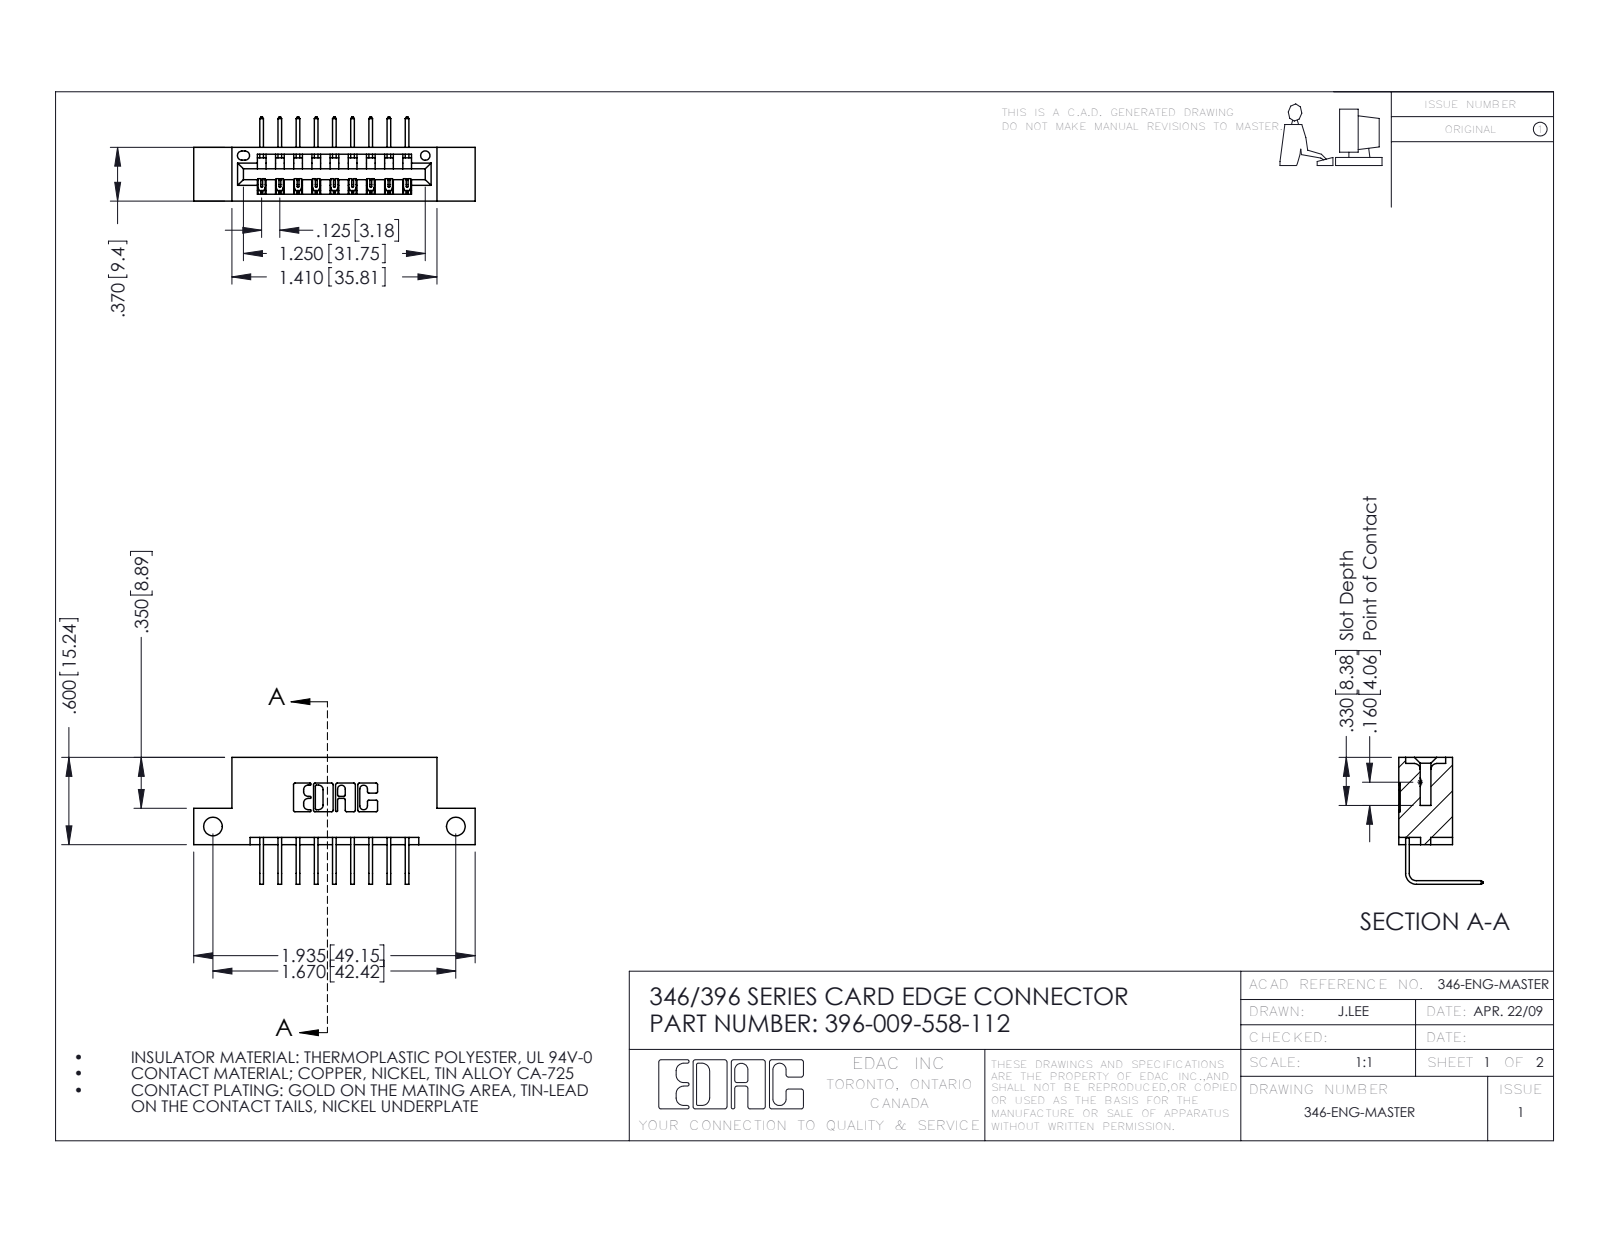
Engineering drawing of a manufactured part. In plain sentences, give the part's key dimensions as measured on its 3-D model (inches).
The part is named "346 Part_Flush Mounting Lugs - Side Mount; 345-292-001_558 Tail - 2; 396-009-558-112". Its 3-D file was written by "SolidWorks 2016 (CONFIG_CONTROL_DESIGN)". It is 10 solids with 662 faces: 454 planar, 208 cylindrical and 0 other. Overall it measures 1.935 by 0.873 by 0.58 inches. Its volume is 0.27 cubic inches and its surface area 8.062 square inches. Round holes: 2 of diameter 0.128, 1 of diameter 0.064. Partial cylindrical surfaces (rounded edges, fillets, slot ends): 22 of radius 0.01, 18 of radius 0.006, 6 of radius 0.007, 6 of radius 0.031, 3 of radius 0.026, 2 of radius 0.031, 2 of radius 0.04, 1 of radius 0.014. The main face-to-face distances are 0.25, 0.322, 0.37, 0.048, 0.298, 0.025, 0.148, 0.222, 0.1, 0.174. The hole center spacings are 1.67.
